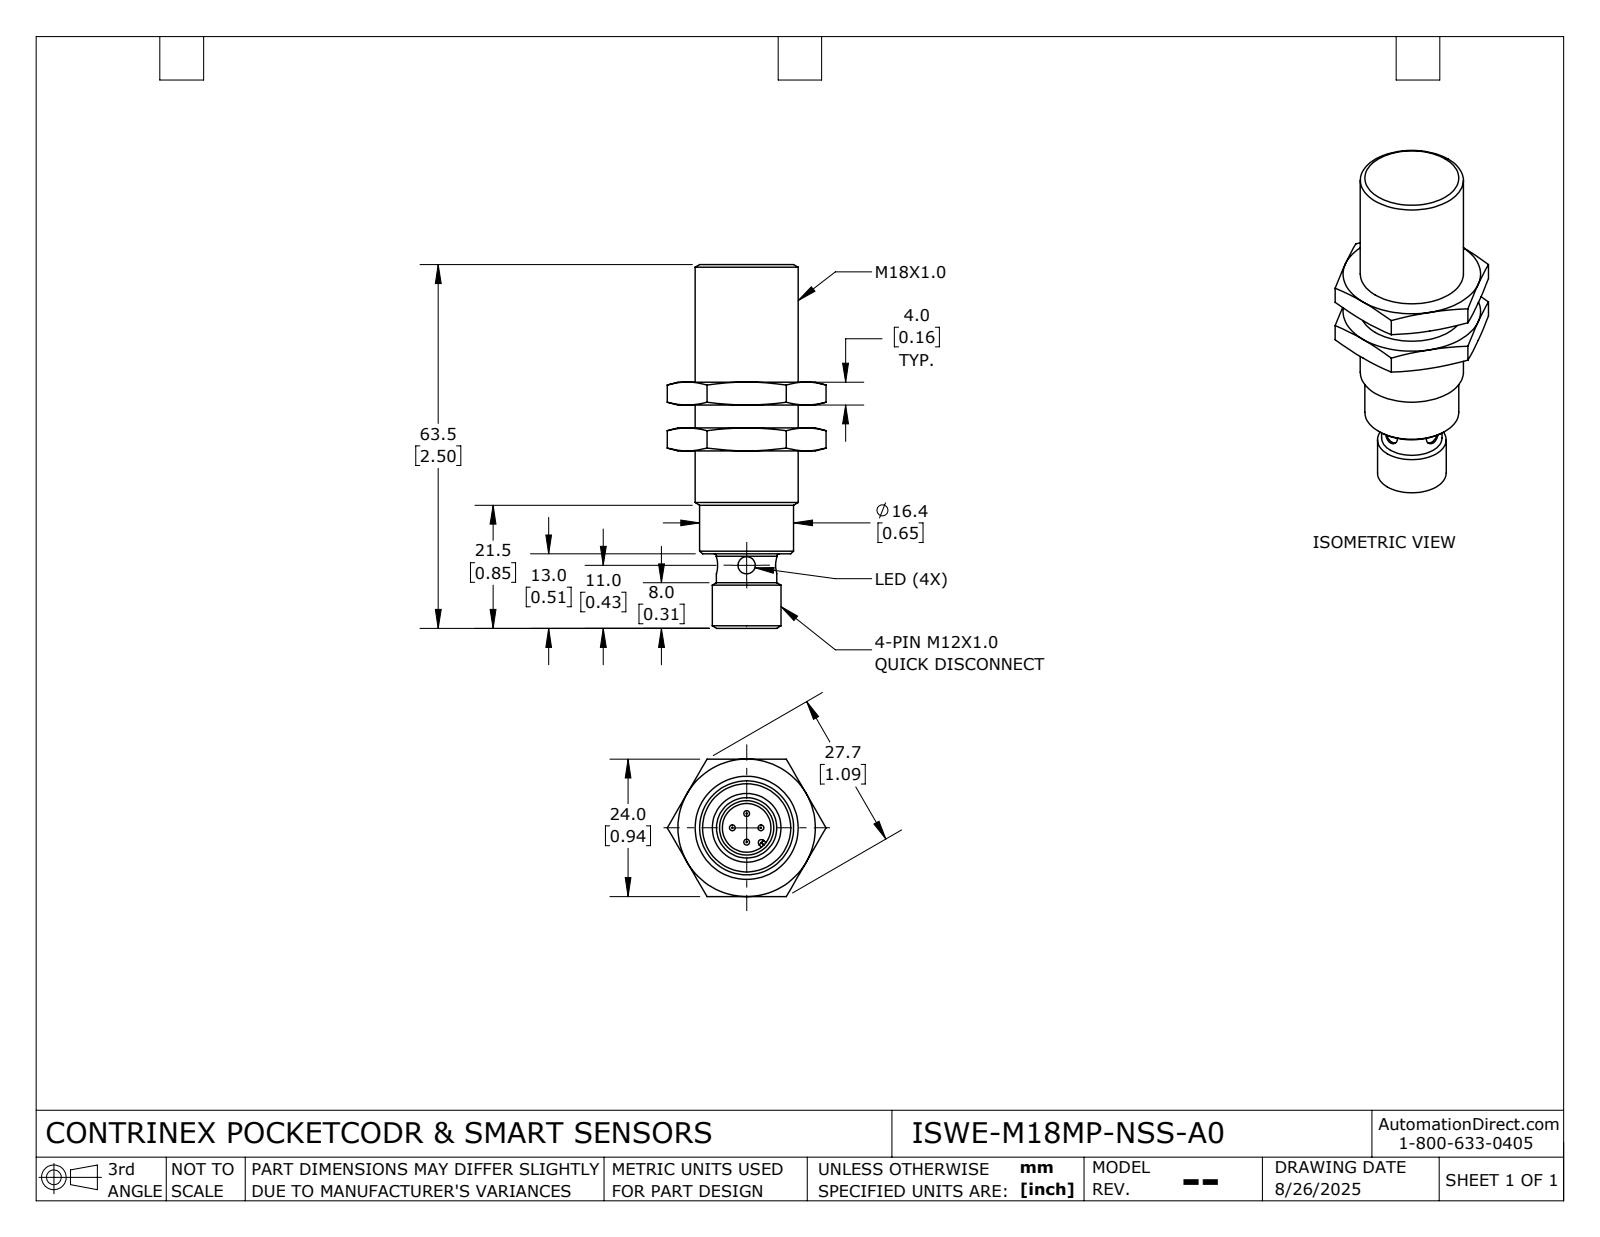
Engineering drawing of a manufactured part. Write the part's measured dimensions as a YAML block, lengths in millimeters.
part_name: "ISWE-M18MP-NSS-A0"
step_written_by: "SolidWorks 2024 (AUTOMOTIVE_DESIGN)"
units: millimeters
bodies: {solids: 3, faces: 89, planar: 31, cylindrical: 18, other: 40}
overall_size: [63.5, 27.7, 24]
volume: 15500
surface_area: 6170
round_holes:
  - {diameter: 3, count: 2}
  - {diameter: 3, count: 1}
  - {diameter: 8.5, count: 1}
  - {diameter: 16.9, count: 1}
round_bosses_or_shafts:
  - {diameter: 1, count: 4}
  - {diameter: 18, count: 1}
  - {diameter: 16.4, count: 1}
  - {diameter: 12, count: 1}
  - {diameter: 10.5, count: 1}
partial_cylinders:
  - {radius: 0.5, count: 2}
  - {radius: 0.5, count: 1}
face_to_face_distances: [4, 8, 24, 12, 24.5, 32.5, 20.5, 28.5, 30, 50.5]
